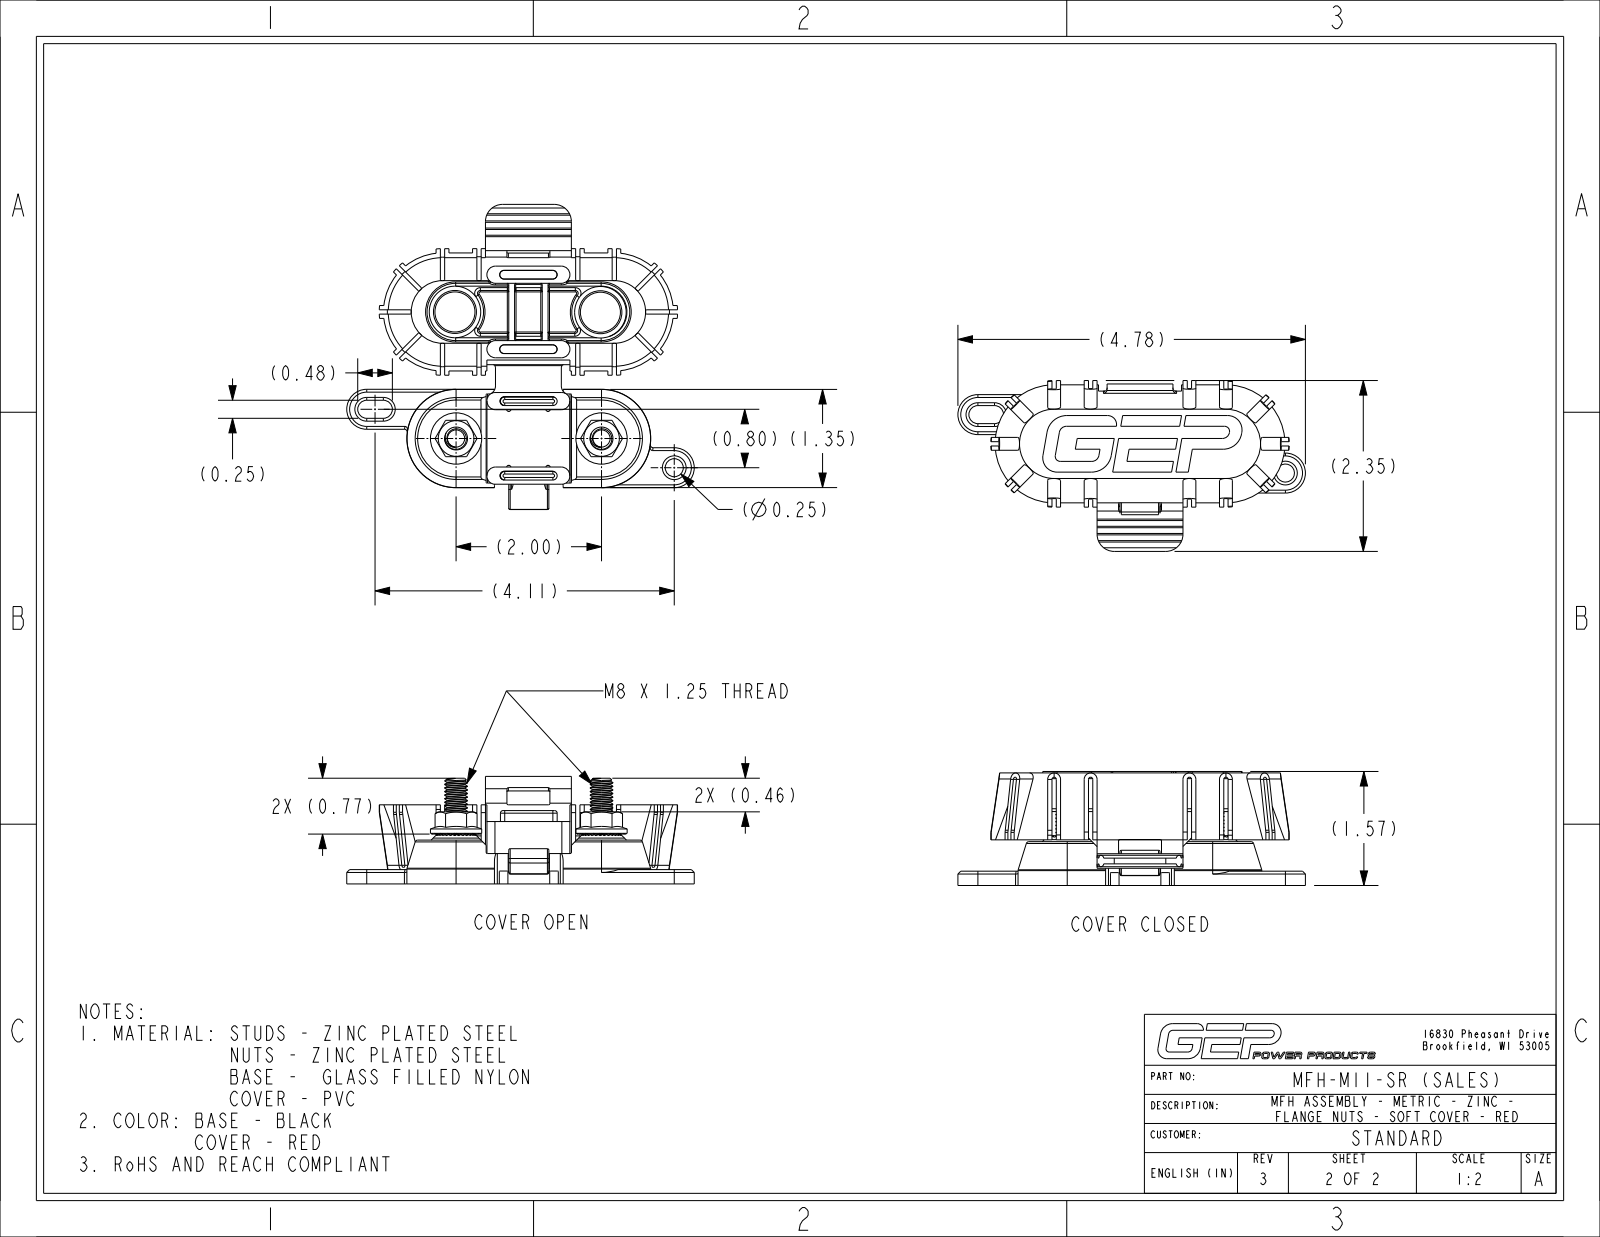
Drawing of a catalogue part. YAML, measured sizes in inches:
part_name: "MFH-MXX-XX_BODY_NCF; C05-1003-M1_NCF; C02-1005-X_NCF; MFH-SR_NCF_INSTALLED (+1 more)"
step_written_by: "CREO PARAMETRIC BY PTC INC, 2024014 (CONFIG_CONTROL_DESIGN)"
units: inches
bodies: {solids: 6, faces: 2343, planar: 929, cylindrical: 749, other: 665}
overall_size: [4.778, 2.348, 1.567]
volume: 3.288
surface_area: 86.97
round_holes:
  - {diameter: 0.244, count: 2}
  - {diameter: 0.354, count: 2}
  - {diameter: 0.591, count: 2}
  - {diameter: 0.248, count: 1}
round_bosses_or_shafts:
  - {diameter: 0.705, count: 2}
  - {diameter: 0.63, count: 2}
  - {diameter: 0.315, count: 2}
partial_cylinders:
  - {radius: 0.016, count: 236}
  - {radius: 0.02, count: 24}
  - {radius: 0.039, count: 20}
  - {radius: 0.02, count: 14}
  - {radius: 0.015, count: 13}
  - {radius: 0.012, count: 10}
  - {radius: 0.035, count: 10}
  - {radius: 0.059, count: 10}
face_to_face_distances: [0.059, 0.118, 0.079, 0.423, 0.177, 0.945, 1.024, 1.13, 0.02, 0.6]
hole_center_spacings: [2, 1.078, 1.087, 1.991, 2.009, 3.027, 3.036]
